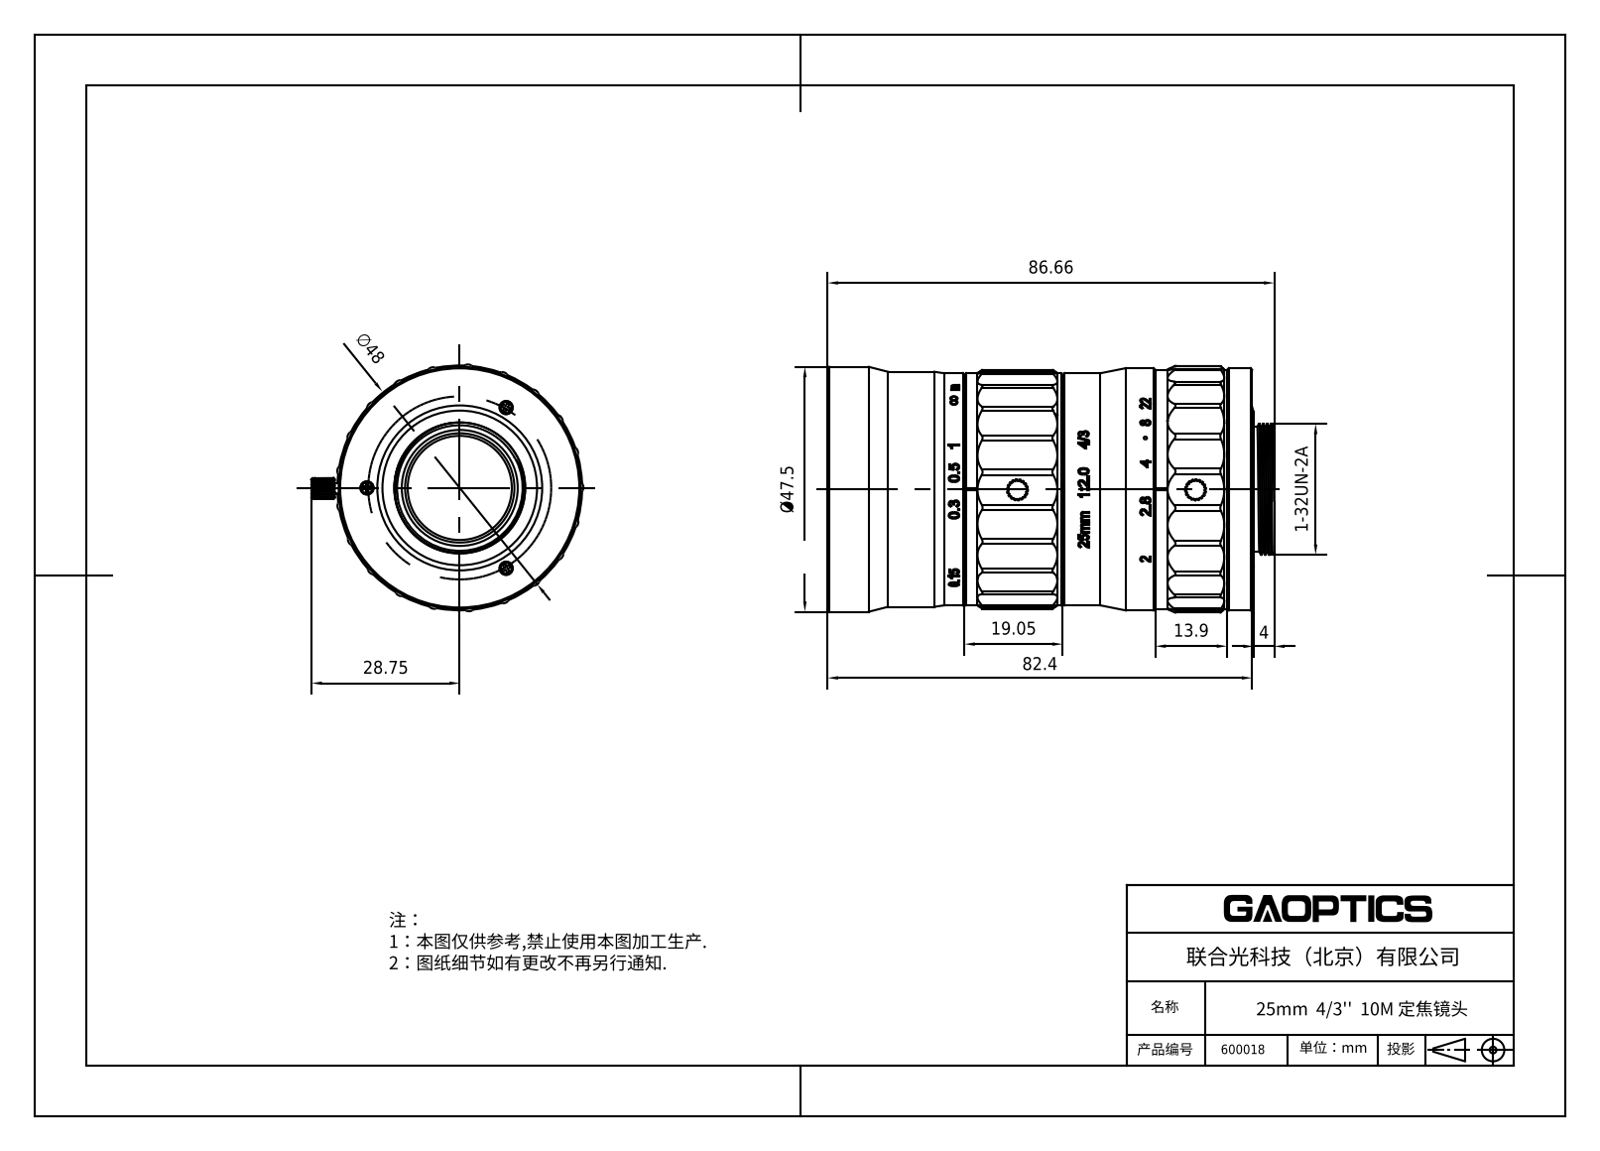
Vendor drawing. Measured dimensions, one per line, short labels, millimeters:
name: 600018
written by: SolidWorks 2020 (CONFIG_CONTROL_DESIGN)
unit: mm
bodies: 8 solids, 1179 faces (0 planar, 0 cylindrical, 1179 other)
size: 86.71 × 52.76 × 47.87
volume: 129 438 mm³; area: 23 861 mm²
